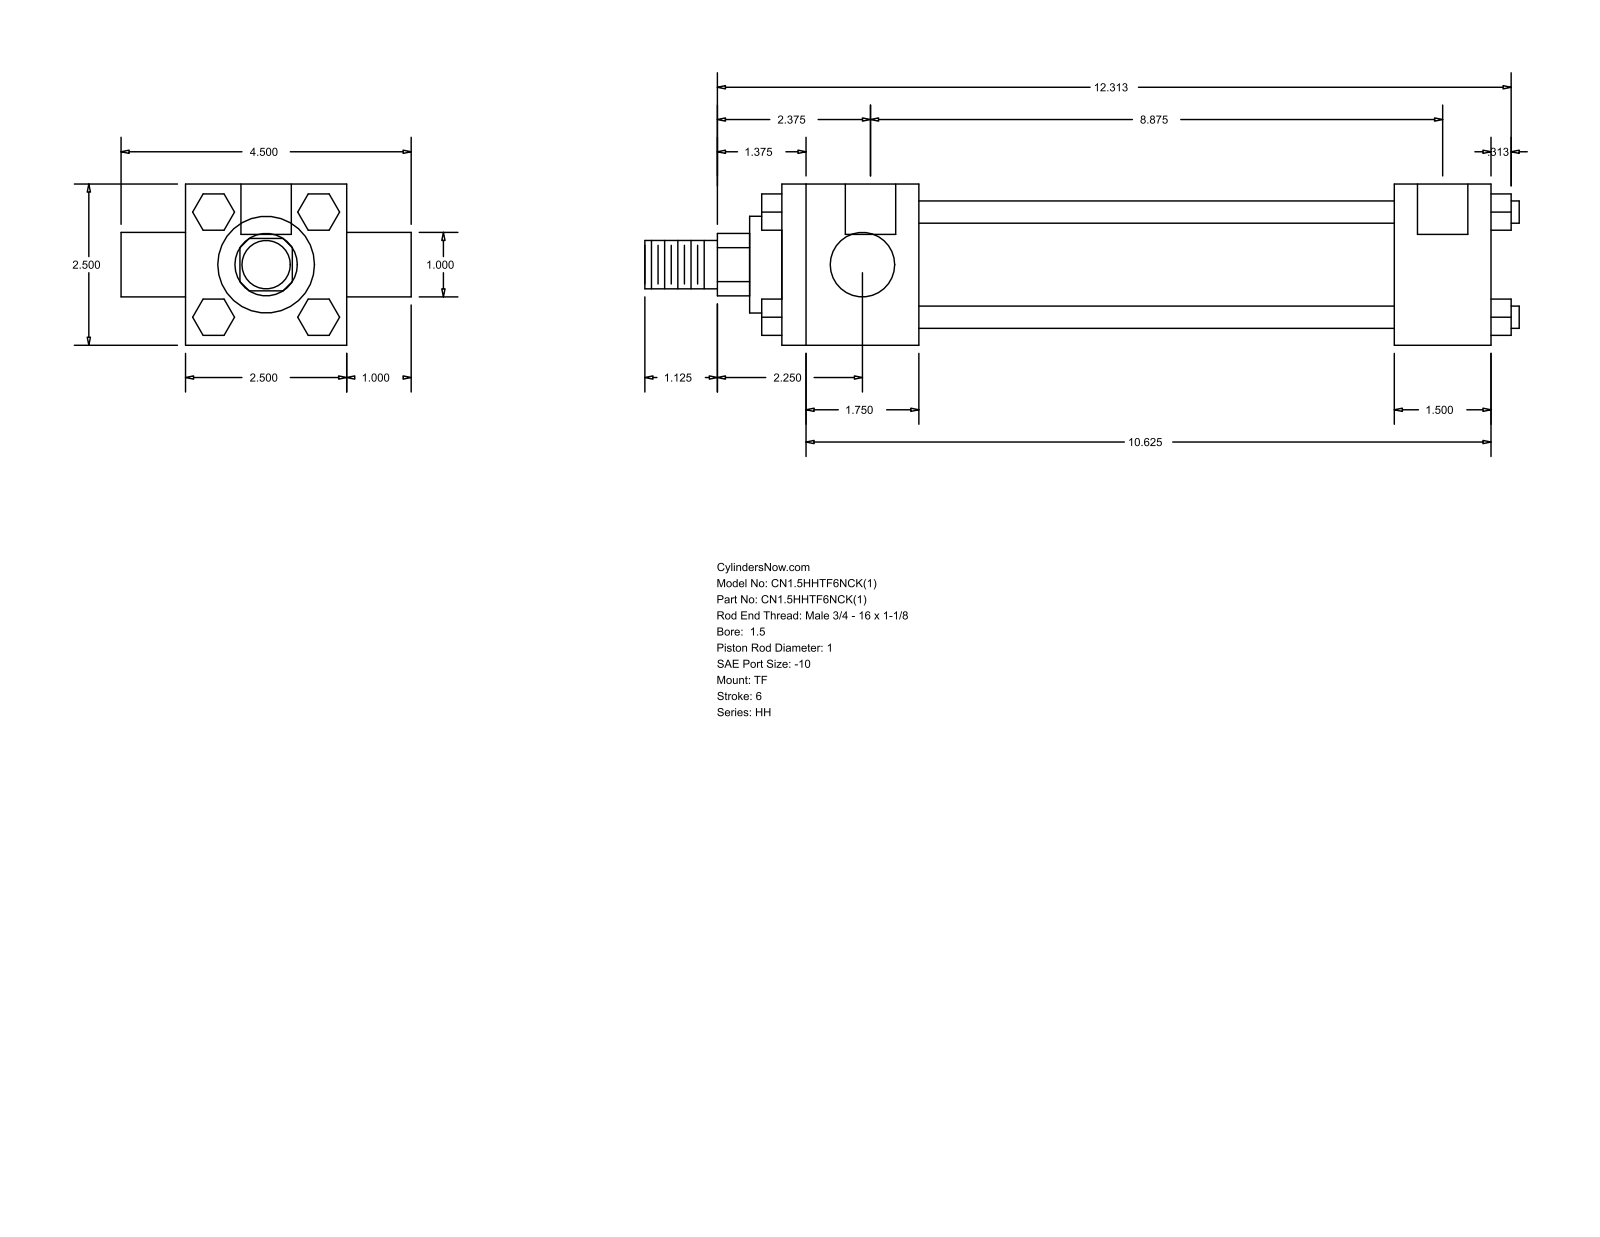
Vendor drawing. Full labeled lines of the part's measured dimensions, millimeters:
Part name (STEP PRODUCT): HH_TF__0150_1
STEP written by: GSSL Pune (CONFIG_CONTROL_DESIGN)
Units: millimetres
Bodies: 0 solids, 120 faces (92 planar, 28 cylindrical, 0 other)
Overall size (bounding box): 344.49 × 114.3 × 63.5
Round holes (diameter × count): ⌀5.56 ×3, ⌀19.84 ×2
Round bosses / shafts (diameter × count): ⌀8.76 ×4, ⌀25.4 ×2, ⌀44.45 ×1, ⌀38.1 ×1, ⌀19.05 ×1
Partial cylindrical surfaces — rounded edges, fillets, slot ends (radius × count): R12.29 ×1
Main face-to-face distances: 63.5, 38.1, 225.42, 187.32, 53.98, 241.3, 279.4, 25.4, 20.7, 14.29
Hole centre spacings: 1.59, 227.01, 225.42, 228.6
